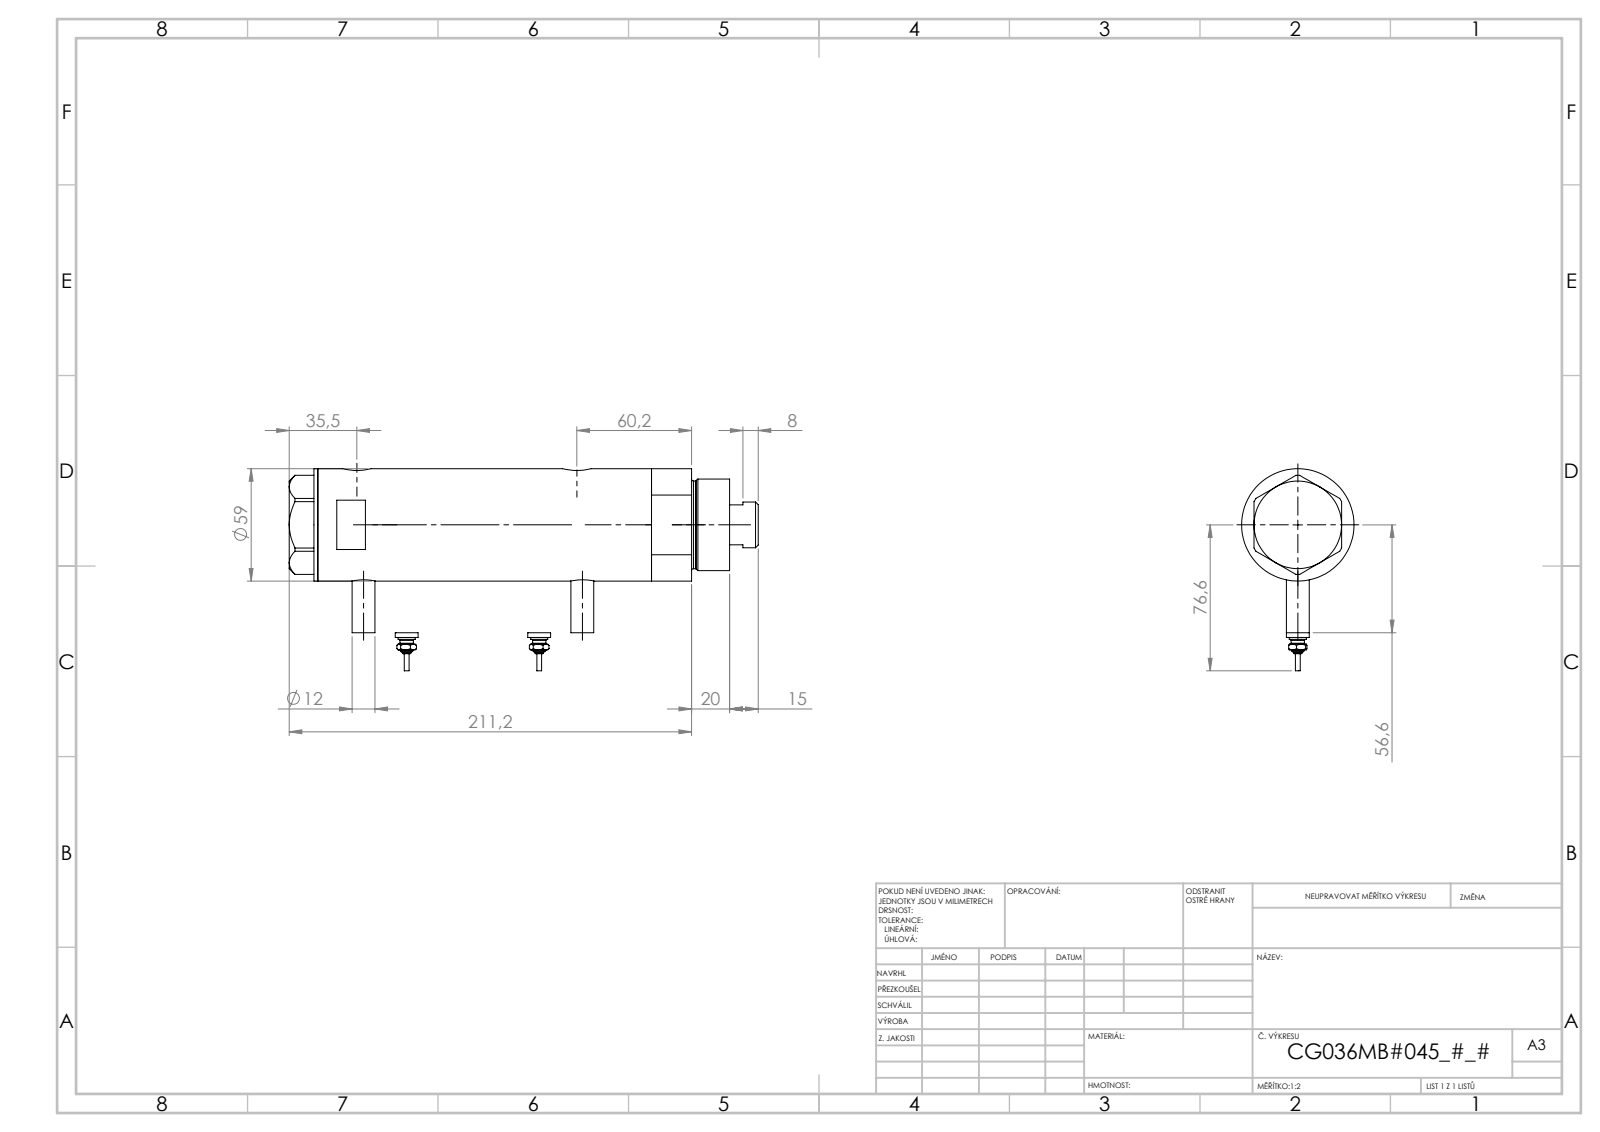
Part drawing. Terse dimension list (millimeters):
name: V270CG_FRONT; Switch; V270CG_BACK; V270CG_MIDDLE (+1 more)
written by: SolidWorks 2019 (CONFIG_CONTROL_DESIGN)
unit: mm
bodies: 6 solids, 212 faces (79 planar, 69 cylindrical, 64 other)
size: 246.2 × 106.1 × 59
volume: 582 782 mm³; area: 117 330 mm²
holes: 2× ⌀9.73, 2× ⌀12.5, 2× ⌀15, 1× ⌀8.5, 1× ⌀25, 1× ⌀26.5, 1× ⌀36, 1× ⌀40, 1× ⌀52
bosses: 4× ⌀12, 2× ⌀9, 2× ⌀7, 2× ⌀4.5, 2× ⌀2.5, 1× ⌀59, 1× ⌀48, 1× ⌀46
face distances: 137.2, 23.5, 113.7, 15, 38.5, 152.2, 2, 231.2, 216.2, 192.7
hole spacings: 2.9, 3.5, 112, 114.9, 115.5, 118.4
